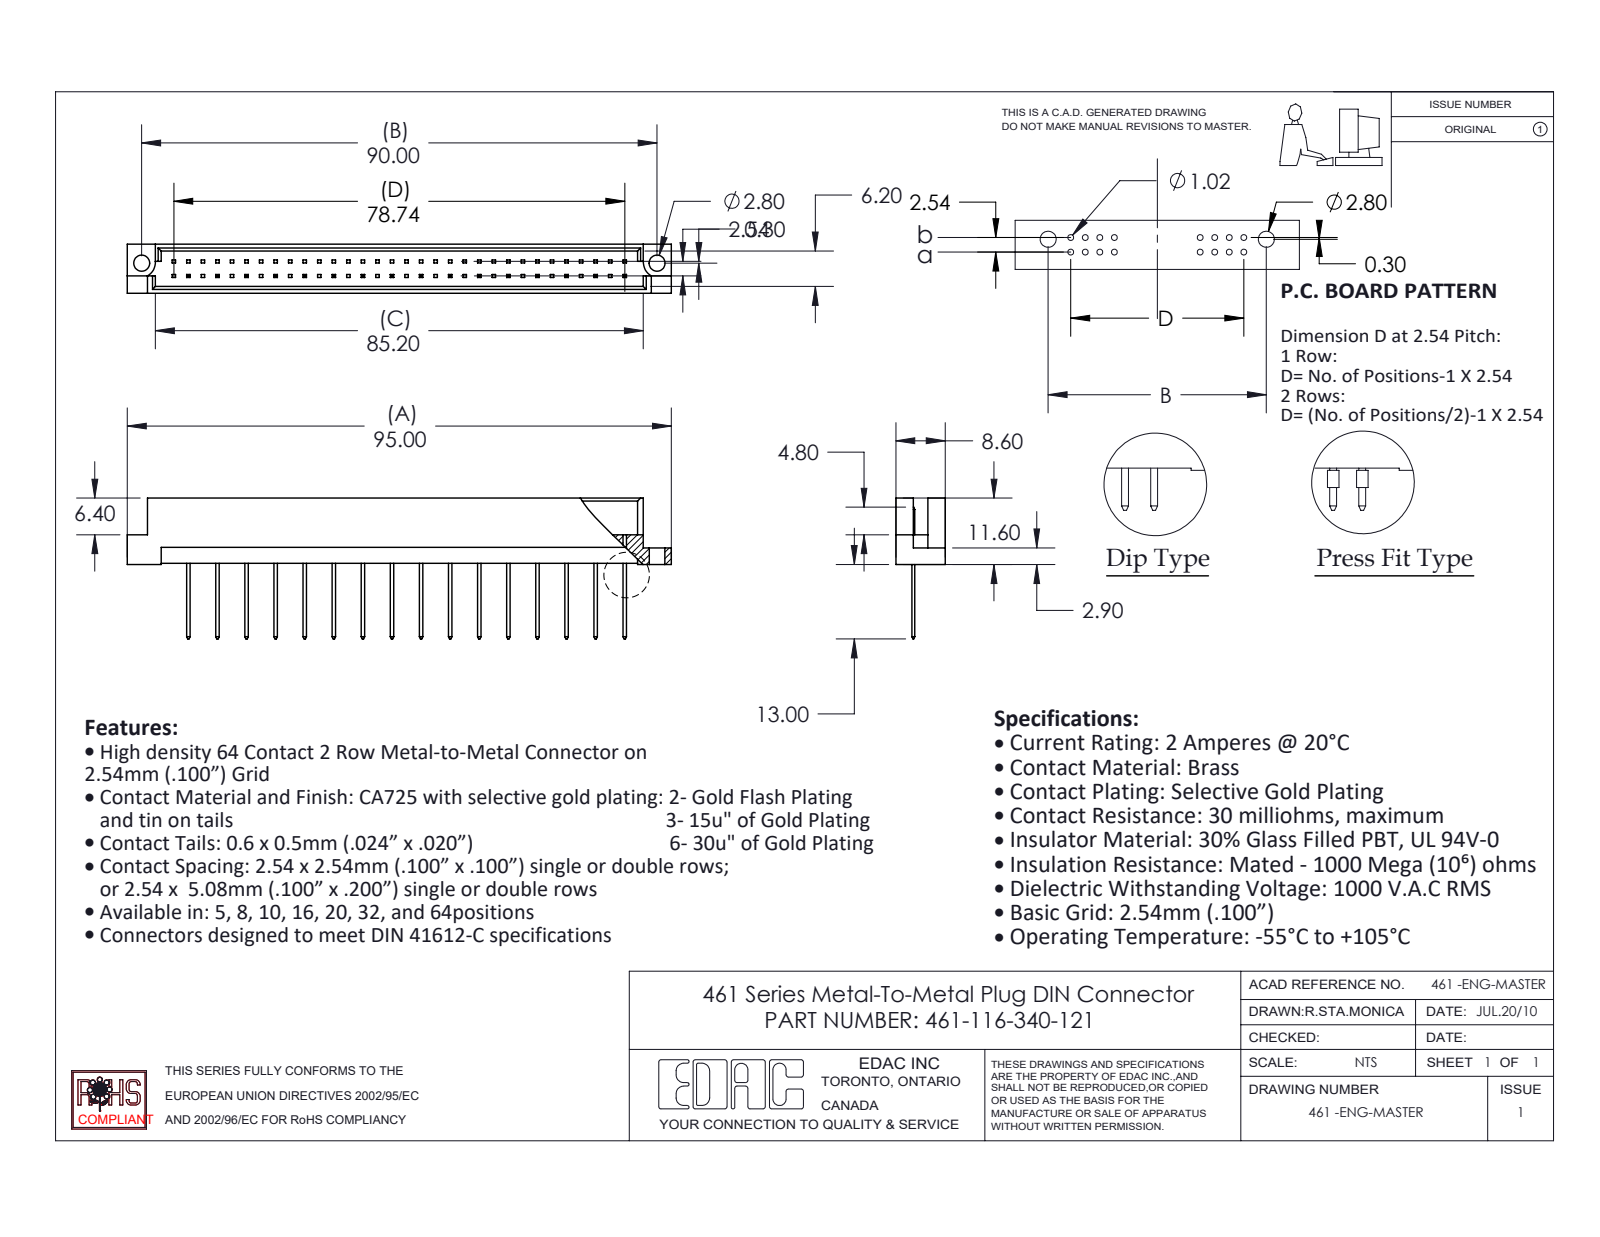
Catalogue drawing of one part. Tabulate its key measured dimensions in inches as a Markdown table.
| quantity | value |
| --- | --- |
| part name | 461 Part_64; 461-290_40; 461-116-340-221 |
| STEP written by | SolidWorks 2020 (CONFIG_CONTROL_DESIGN) |
| units | inches |
| bodies | 17 solids, 529 faces (522 planar, 7 cylindrical, 0 other) |
| overall size | 3.74 × 0.969 × 0.339 |
| volume | 0.291 in³ |
| surface area | 10.04 in² |
| round holes (diameter × count) | 0.11 × 2 |
| partial cylindrical surfaces (radius × count) | 0.11 × 2 |
| main face-to-face distances | 0.047, 0.291, 0.339, 0.244, 0.197, 0.129, 0.209, 0.082, 0.162, 0.109 |
| hole center spacings | 3.543 |
